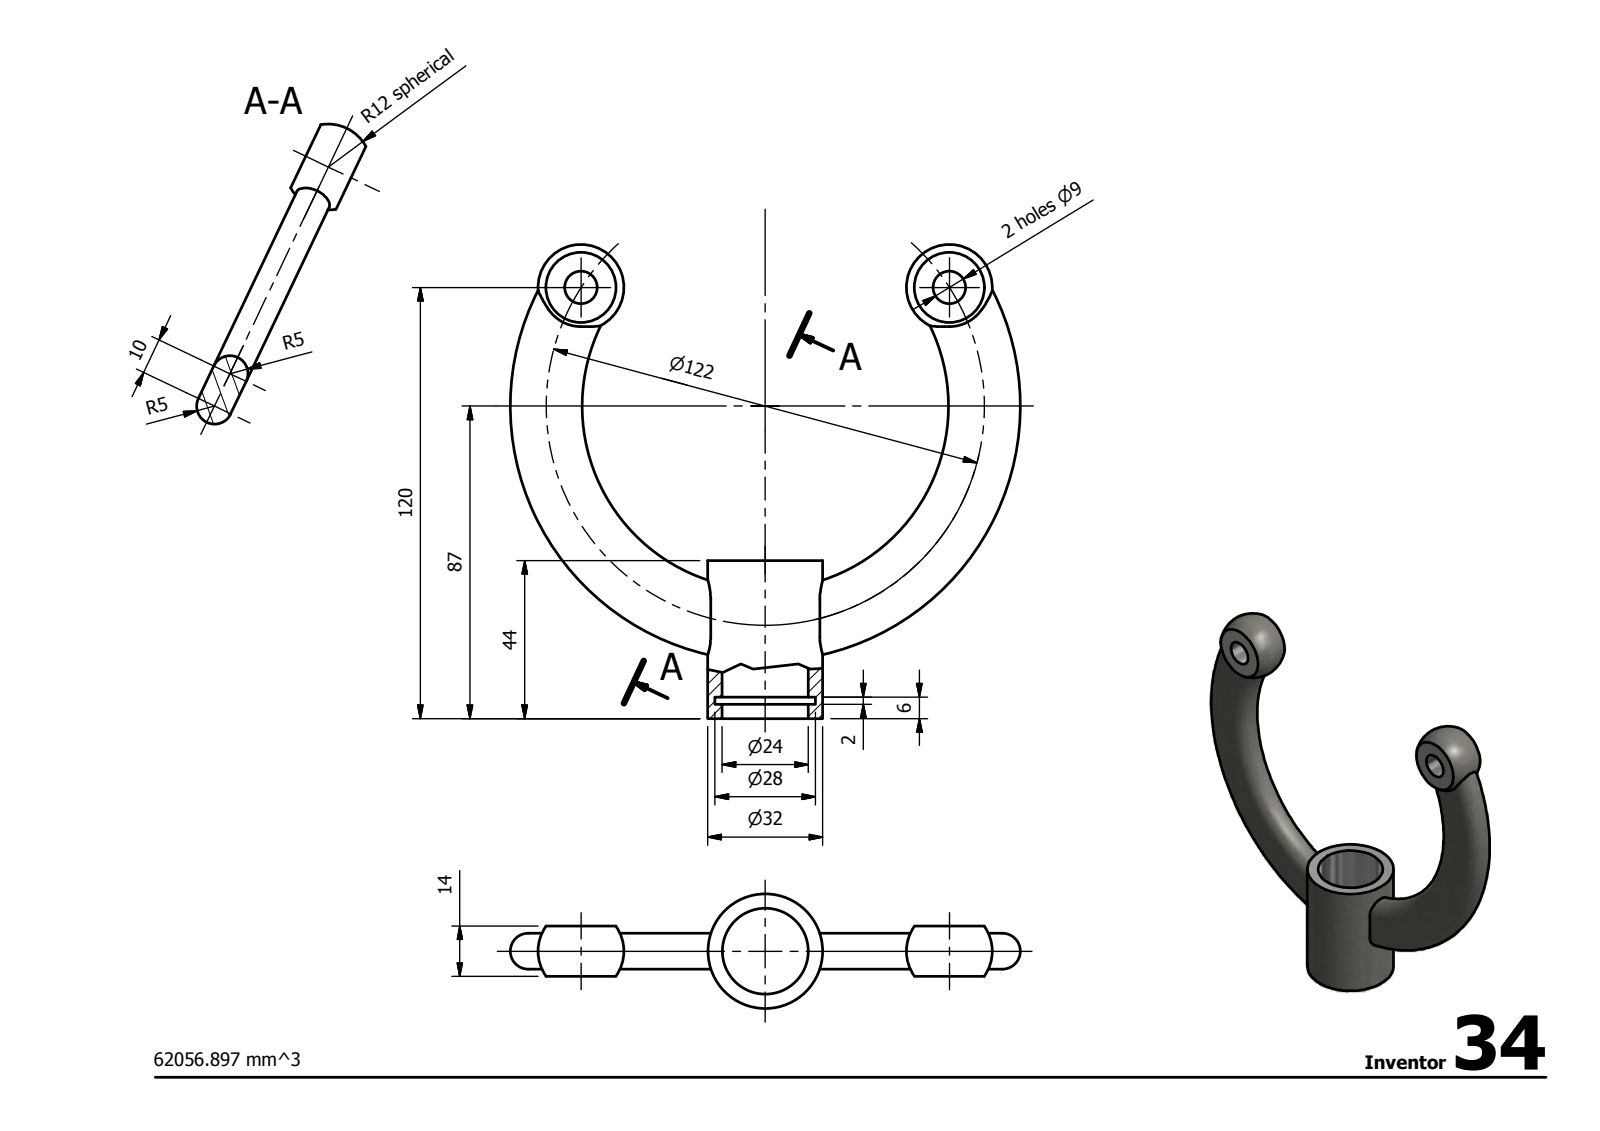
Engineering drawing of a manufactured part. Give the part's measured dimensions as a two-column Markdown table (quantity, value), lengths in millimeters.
| quantity | value |
| --- | --- |
| STEP written by | Autodesk Inventor 2014 (AUTOMOTIVE_DESIGN) |
| units | millimeters |
| bodies | 1 solid, 24 faces (12 planar, 6 cylindrical, 6 other) |
| overall size | 142 × 132 × 32 |
| volume | 61 877 mm³ |
| surface area | 22 761 mm² |
| round holes (diameter × count) | 9 × 2, 24 × 1, 28 × 1 |
| round bosses / shafts (diameter × count) | 32 × 1 |
| main face-to-face distances | 10, 2, 12, 14, 44, 4, 40, 6, 38 |
| hole center spacings | 102.6 |
